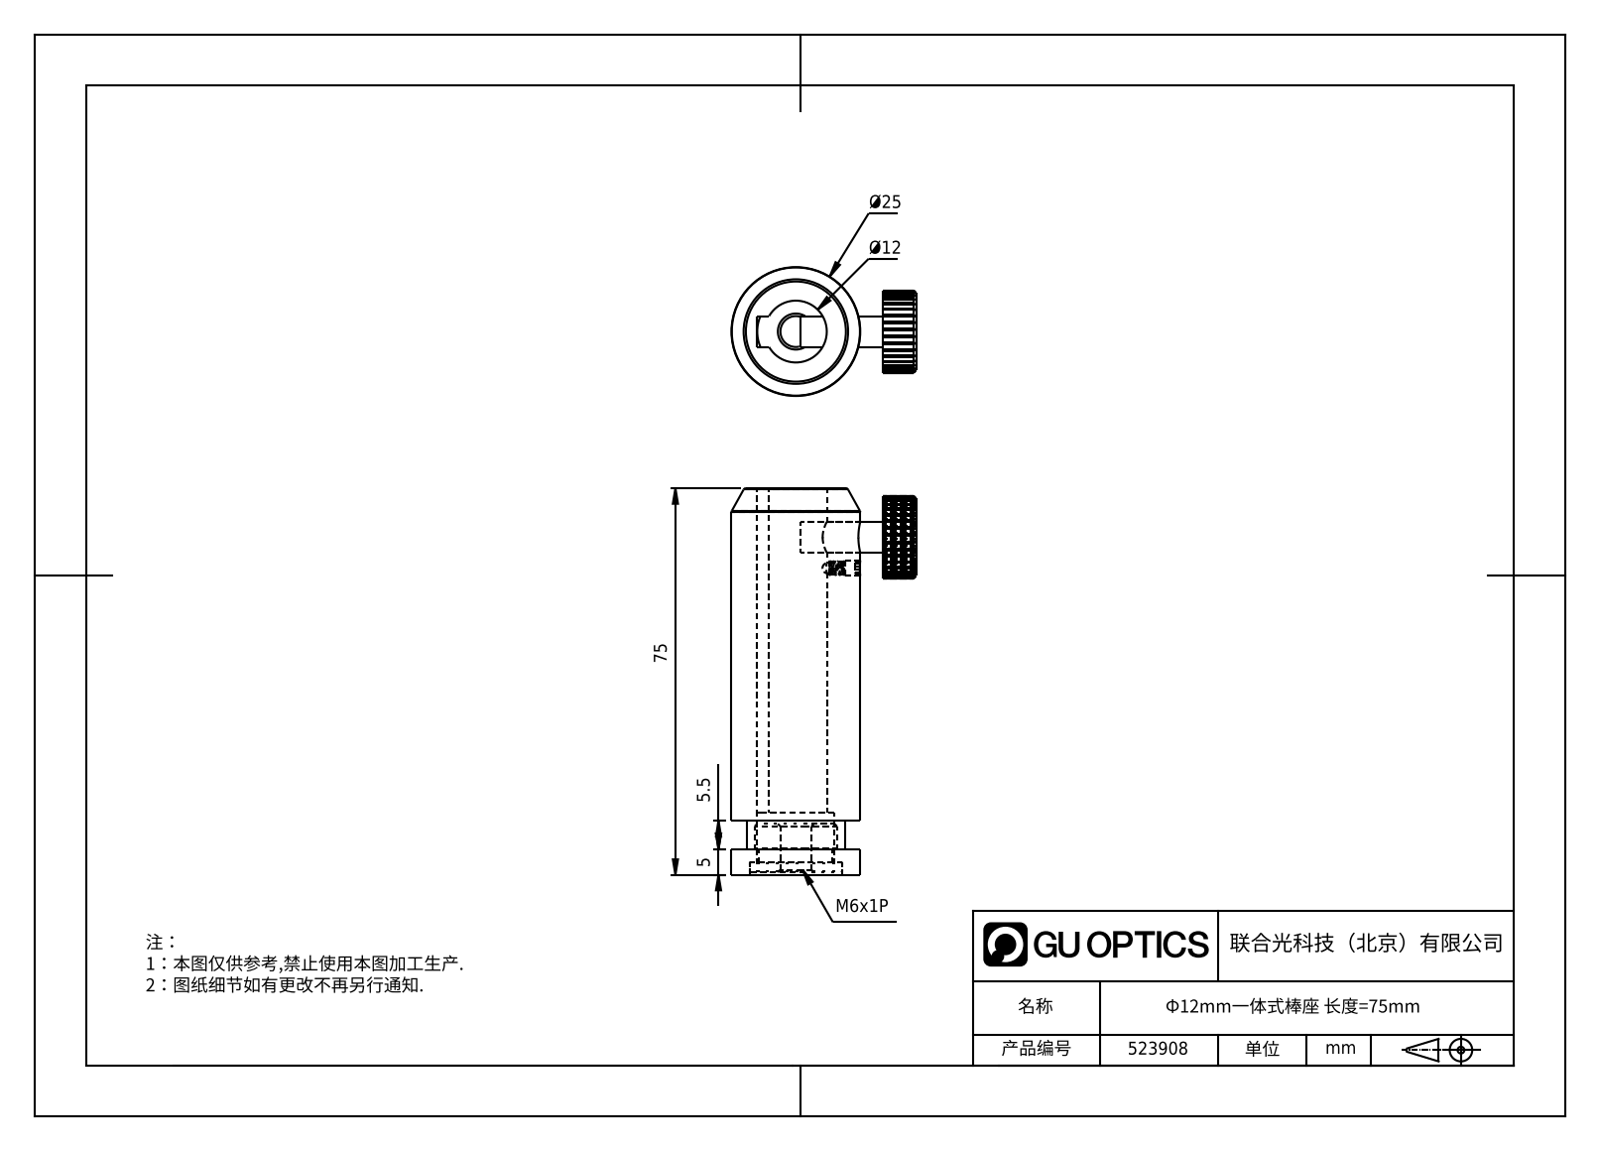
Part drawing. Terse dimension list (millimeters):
name: M-PHF-12-75
written by: SolidWorks 2019 (CONFIG_CONTROL_DESIGN)
unit: mm
bodies: 3 solids, 217 faces (114 planar, 81 cylindrical, 22 other)
size: 75 × 35.84 × 25
volume: 28 010 mm³; area: 11 435 mm²
holes: 1× ⌀2.1, 1× ⌀2.12, 1× ⌀2.6, 1× ⌀6, 1× ⌀12, 1× ⌀15, 1× ⌀18
bosses: 1× ⌀25, 1× ⌀19, 1× ⌀14.3, 1× ⌀6, 1× ⌀3, 1× ⌀2.16, 1× ⌀0.99
rounds: 1× R8
face distances: 5, 10.5, 5.5, 0.5, 4.5, 10, 75, 74.5, 70, 64.5
